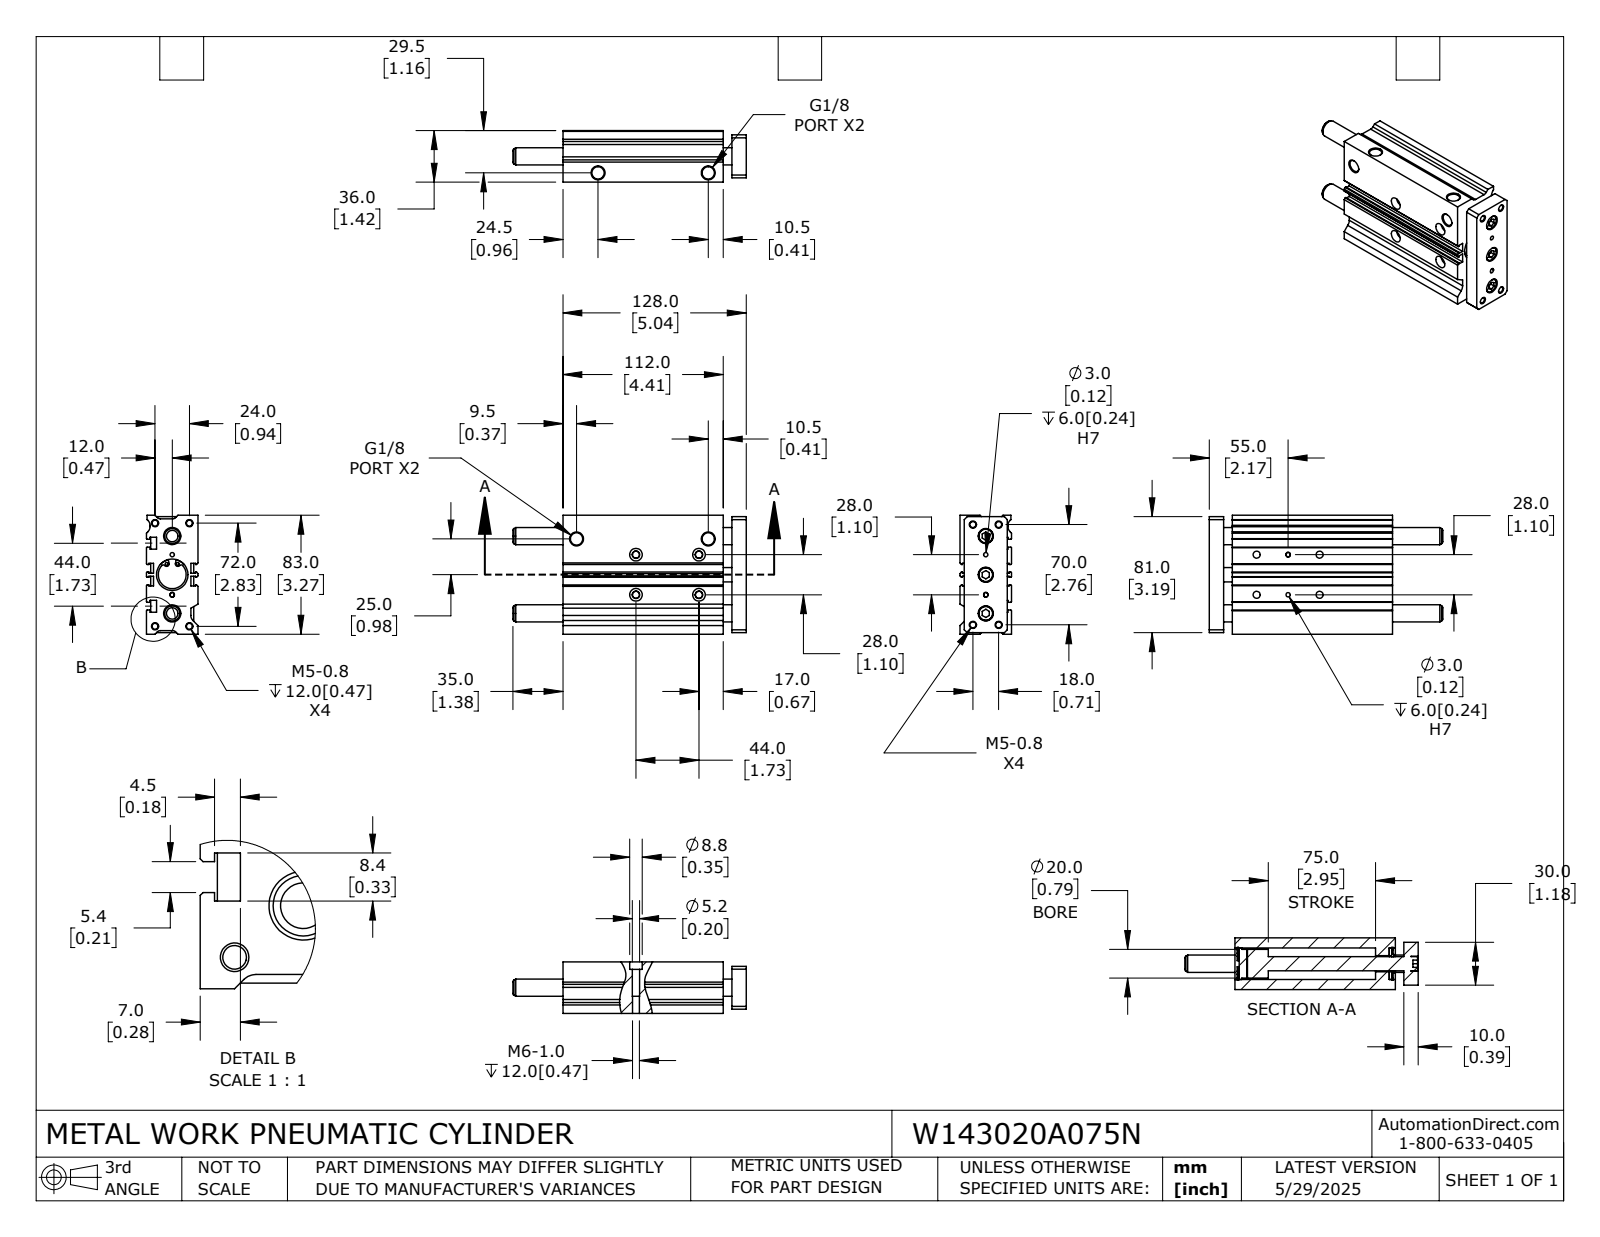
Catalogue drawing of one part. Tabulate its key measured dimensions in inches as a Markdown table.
| quantity | value |
| --- | --- |
| part name | W143020A075N_BODY; W143020A075N_ROD; W143020A075N |
| STEP written by | SolidWorks 2024 (CONFIG_CONTROL_DESIGN) |
| units | inches |
| bodies | 6 solids, 357 faces (174 planar, 145 cylindrical, 38 other) |
| overall size | 6.417 × 3.268 × 1.417 |
| volume | 17.94 in³ |
| surface area | 138.1 in² |
| round holes (diameter × count) | 0.163 × 8, 0.079 × 4, 0.118 × 4, 0.205 × 4, 0.337 × 4, 0.346 × 4, 0.413 × 3, 0.194 × 2, 0.194 × 2, 0.472 × 2, 0.449 × 1, 0.767 × 1 |
| round bosses / shafts (diameter × count) | 0.394 × 3, 0.906 × 2, 0.787 × 1, 0.512 × 1 |
| partial cylindrical surfaces (radius × count) | 0.053 × 4, 0.059 × 4, 0.071 × 4, 0.118 × 4, 0.197 × 3 |
| main face-to-face distances | 1.417, 0.098, 0.197, 1.22, 0.079, 1.024, 0.394, 3.268, 0.236, 0.63 |
| hole center spacings | 0.124, 0.296, 0.336, 0.474, 0.591, 0.78, 0.828, 0.864 |
